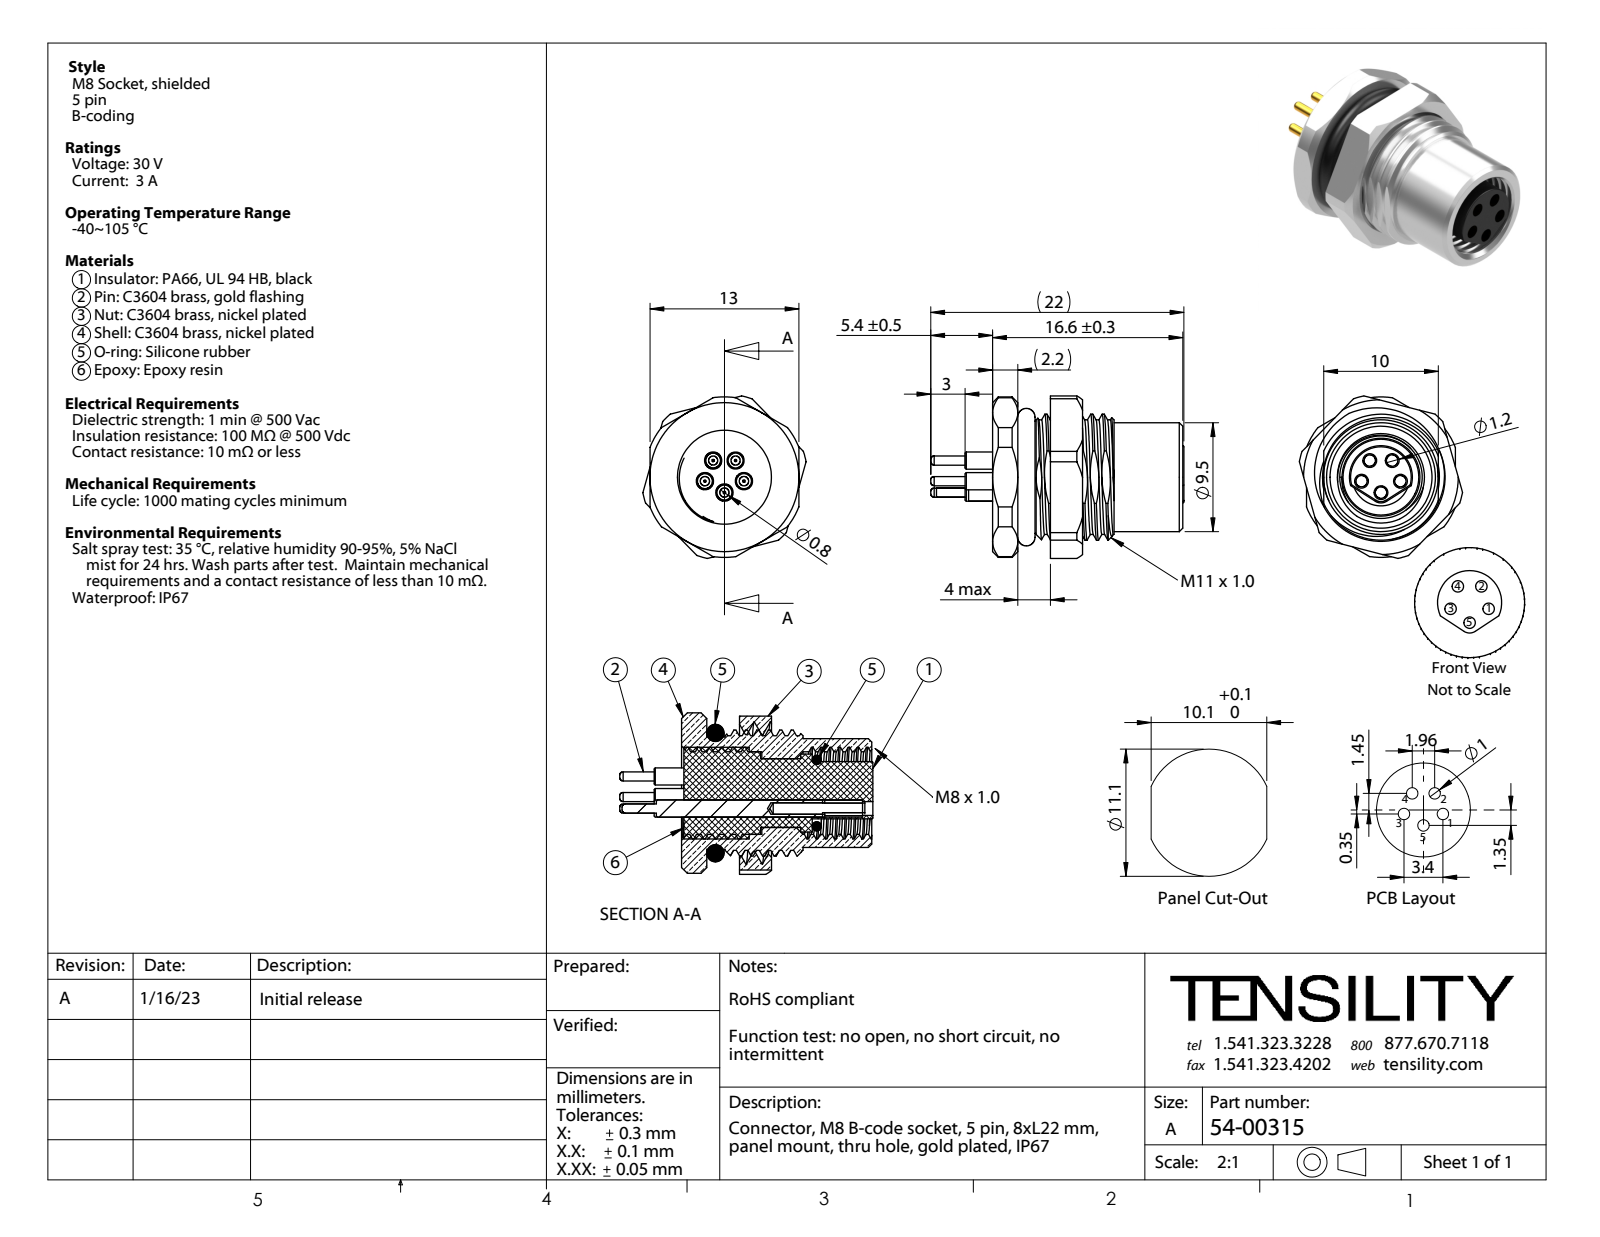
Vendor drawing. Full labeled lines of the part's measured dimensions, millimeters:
Part name (STEP PRODUCT): 54-00315-01; 54-00315-03; 54-00315-07; 54-00315-04 (+3 more)
STEP written by: SolidWorks 2021 (CONFIG_CONTROL_DESIGN)
Units: millimetres
Bodies: 11 solids, 468 faces (122 planar, 200 cylindrical, 146 other)
Overall size (bounding box): 22.1 × 14.25 × 14.19
Volume: 1 528 mm³ · Surface area: 3 496 mm²
Round holes (diameter × count): ⌀1 ×5, ⌀1.2 ×5, ⌀6 ×1, ⌀7.2 ×1, ⌀8 ×1, ⌀10.2 ×1
Round bosses / shafts (diameter × count): ⌀1.5 ×5, ⌀0.8 ×5, ⌀10 ×1, ⌀9.8 ×1, ⌀9.5 ×1, ⌀6.8 ×1
Partial cylindrical surfaces — rounded edges, fillets, slot ends (radius × count): R0.1 ×2, R0.9 ×1, R2.75 ×1, R5.5 ×1, R7 ×1, R7.25 ×1
Main face-to-face distances: 13, 2.2, 2, 5.05, 4.85, 2.85, 7.85, 7.65, 5.65, 2.8
Hole centre spacings: 1.74, 1.75, 1.94, 1.97, 2.97, 3.23, 1.35, 1.96
